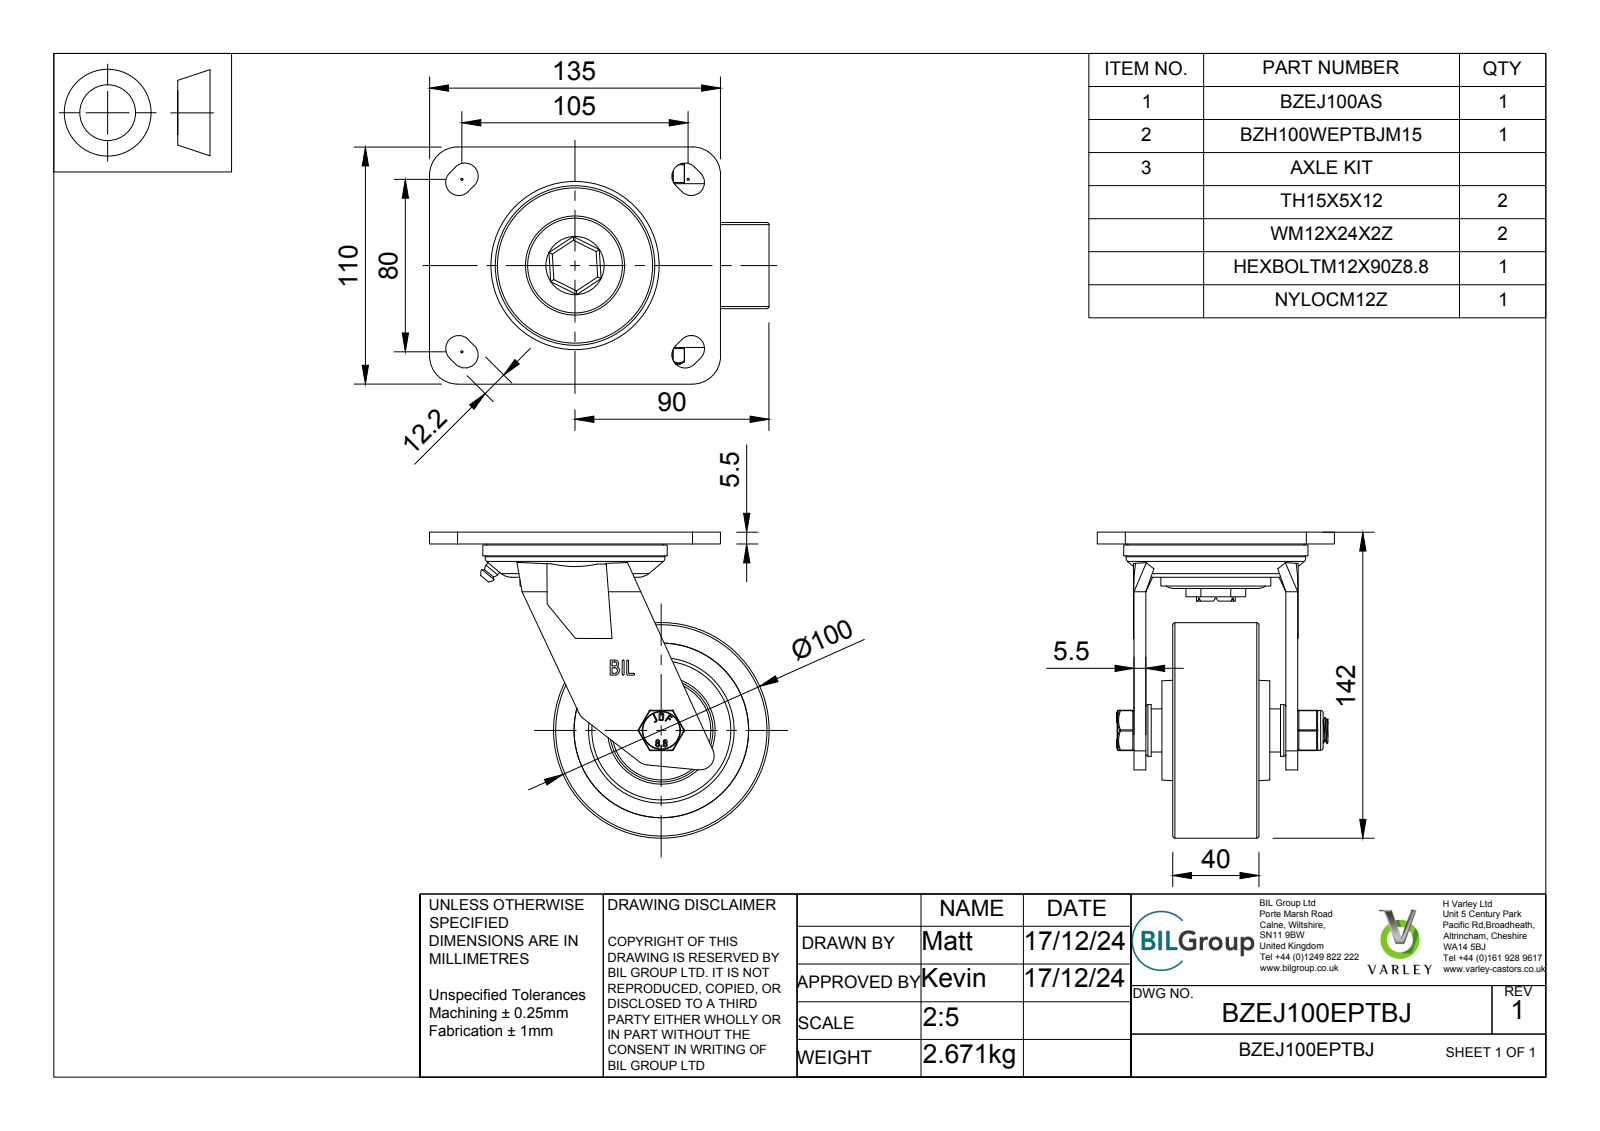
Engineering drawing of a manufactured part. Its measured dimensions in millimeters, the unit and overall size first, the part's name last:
Units: millimetres
Overall size (bounding box): 157.5 × 142 × 110
Round holes (diameter × count): ⌀12 ×1, ⌀12.5 ×1, ⌀13 ×1, ⌀14 ×1, ⌀15 ×1, ⌀18 ×1, ⌀20.5 ×1, ⌀26 ×1, ⌀26.8 ×1, ⌀28 ×1, ⌀28.2 ×1, ⌀32 ×1
Round bosses / shafts (diameter × count): ⌀100 ×1, ⌀85.5 ×1, ⌀51 ×1, ⌀24 ×1, ⌀21.5 ×1, ⌀20 ×1, ⌀19 ×1, ⌀18.5 ×1
Partial cylindrical surfaces — rounded edges, fillets, slot ends (radius × count): R0.5 ×23, R6.1 ×8, R1.5 ×6, R0.47 ×4, R0.9 ×4, R13 ×4, R0.89 ×2, R0.89 ×2
Main face-to-face distances: 5.5, 18, 12.5, 52.5, 0.5, 70.5, 58, 13, 45, 5
Volume: 488 724 mm³ · Surface area: 171 612 mm²
Bodies: 45 solids, 1215 faces (463 planar, 214 cylindrical, 538 other)
Part name (STEP PRODUCT): BZEJ100EPTBJ v3; BZEJ100AS v1; FABRICATED STEEL TOP PLATE; FABRICATED STEEL TOP PLATE Geometry (+8 more)
STEP written by: Autodesk Translation Framework v13.20.0.188 (AP242_MANAGED_MODEL_BASED_3D_ENGINEERING_MIM_LF)
